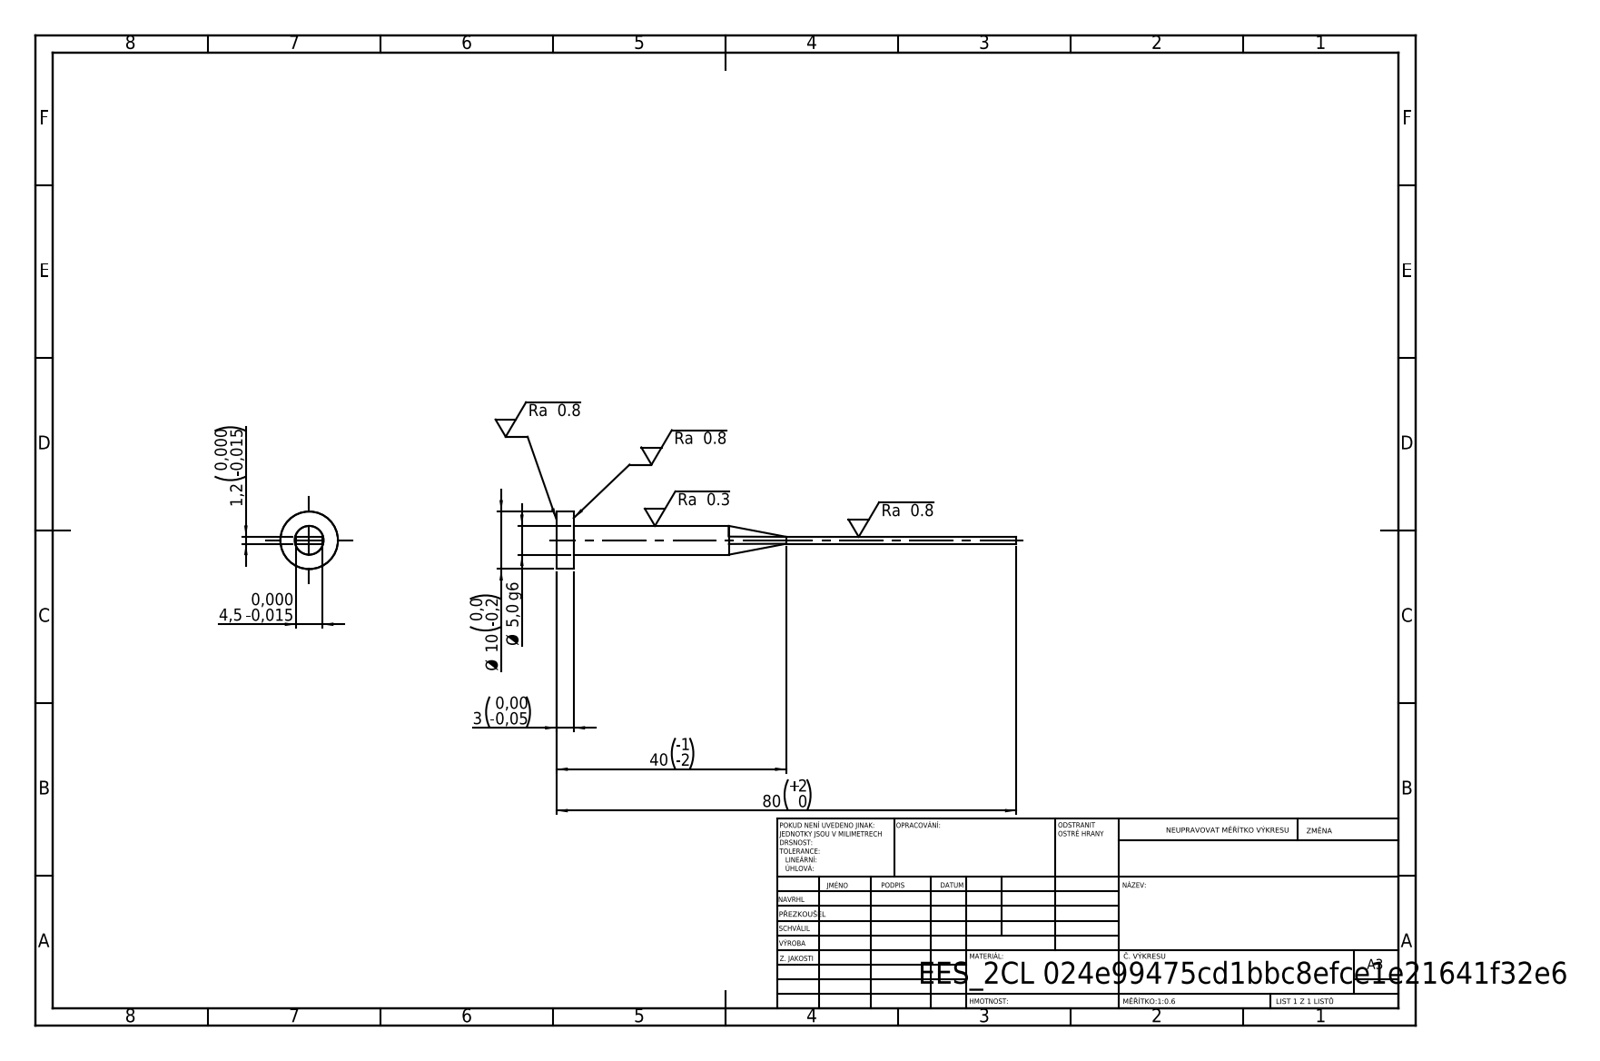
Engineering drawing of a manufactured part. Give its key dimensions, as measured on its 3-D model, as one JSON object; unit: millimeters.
{"step_written_by": "SolidWorks 2019 (CONFIG_CONTROL_DESIGN)", "units": "millimeters", "bodies": {"solids": 1, "faces": 15, "planar": 7, "cylindrical": 4, "other": 4}, "overall_size": [80, 10, 10], "volume_mm3": 1102, "surface_area_mm2": 1248, "round_bosses_or_shafts": [[10, 1], [5, 1]], "face_to_face_distances": [1.2, 3, 4.5, 80, 77]}
